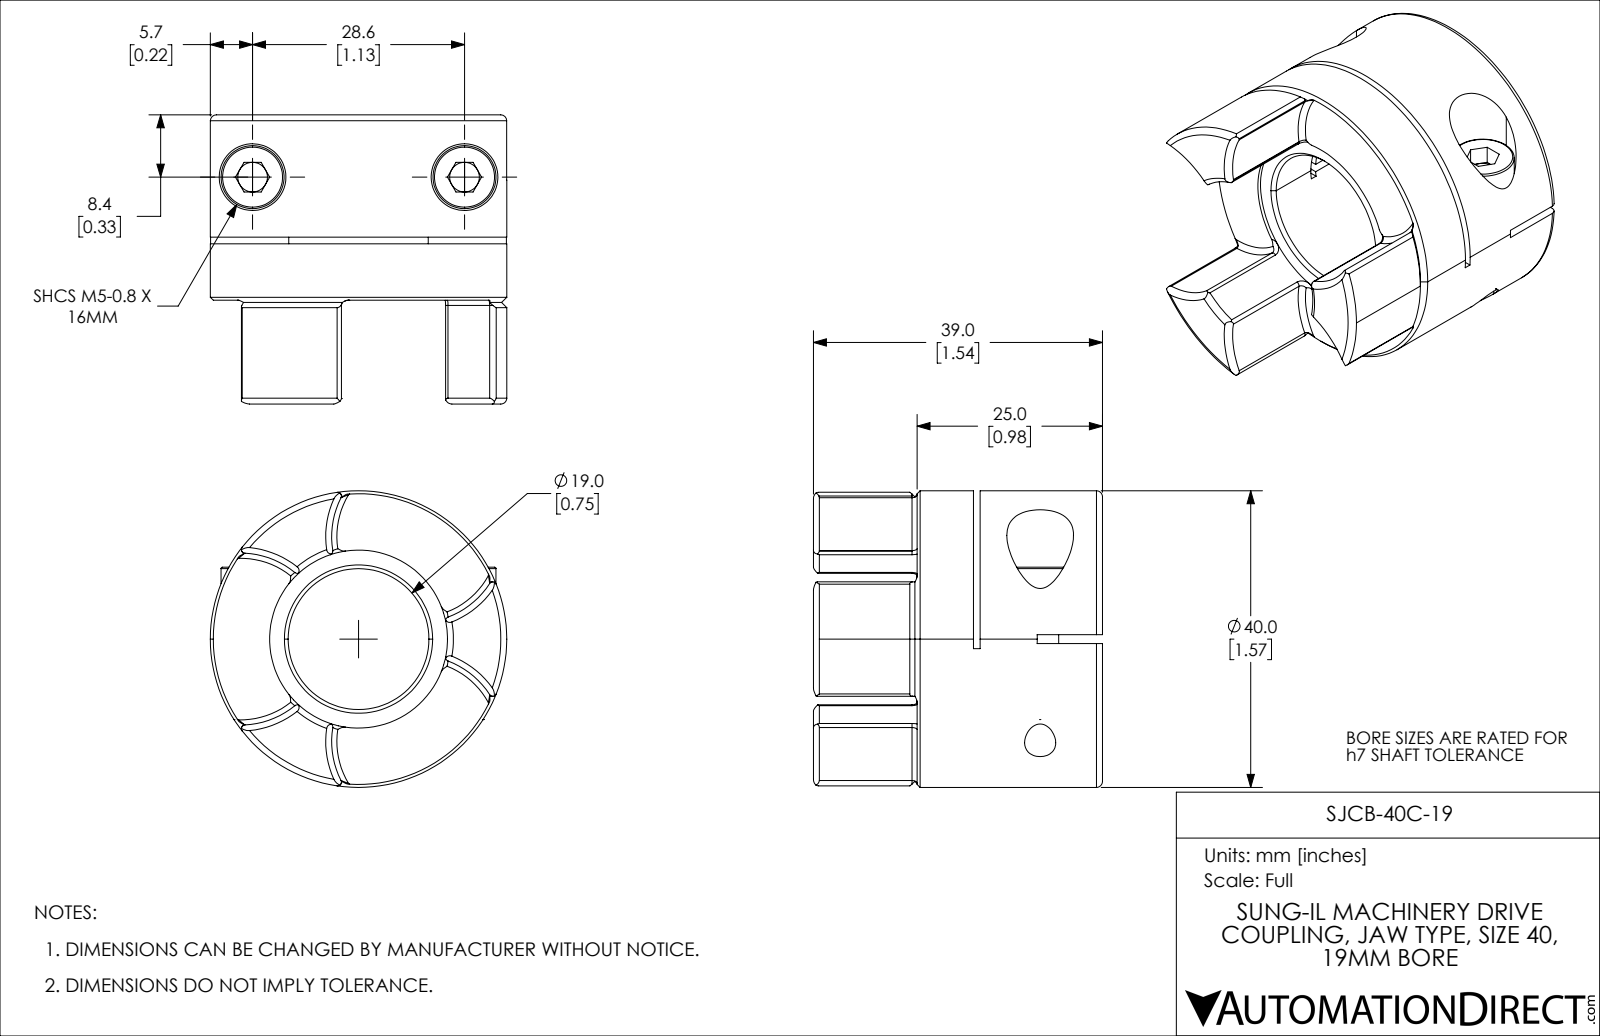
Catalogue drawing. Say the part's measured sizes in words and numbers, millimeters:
The part is named "SJCB-40C-19". Its 3-D file was written by "SolidWorks 2021 (CONFIG_CONTROL_DESIGN)". It is 3 solids with 184 faces: 50 planar, 68 cylindrical and 66 other. Overall it measures 40 by 40 by 39 millimeters. Its volume is 26 193 cubic millimeters and its surface area 11 331 square millimeters. Round holes: 2 of diameter 4, 2 of diameter 4.2, 2 of diameter 5.4, 2 of diameter 9, 1 of diameter 19, 1 of diameter 24. Round bosses or shafts: 2 of diameter 8.5, 2 of diameter 5, 1 of diameter 40. Partial cylindrical surfaces (rounded edges, fillets, slot ends): 12 of radius 0.5, 3 of radius 11.6, 1 of radius 40. The main face-to-face distances are 17.4, 0.9, 16.5, 8.5, 7.6, 25, 1.2, 14, 21.6, 22.5. The hole center spacings are 28.6.
